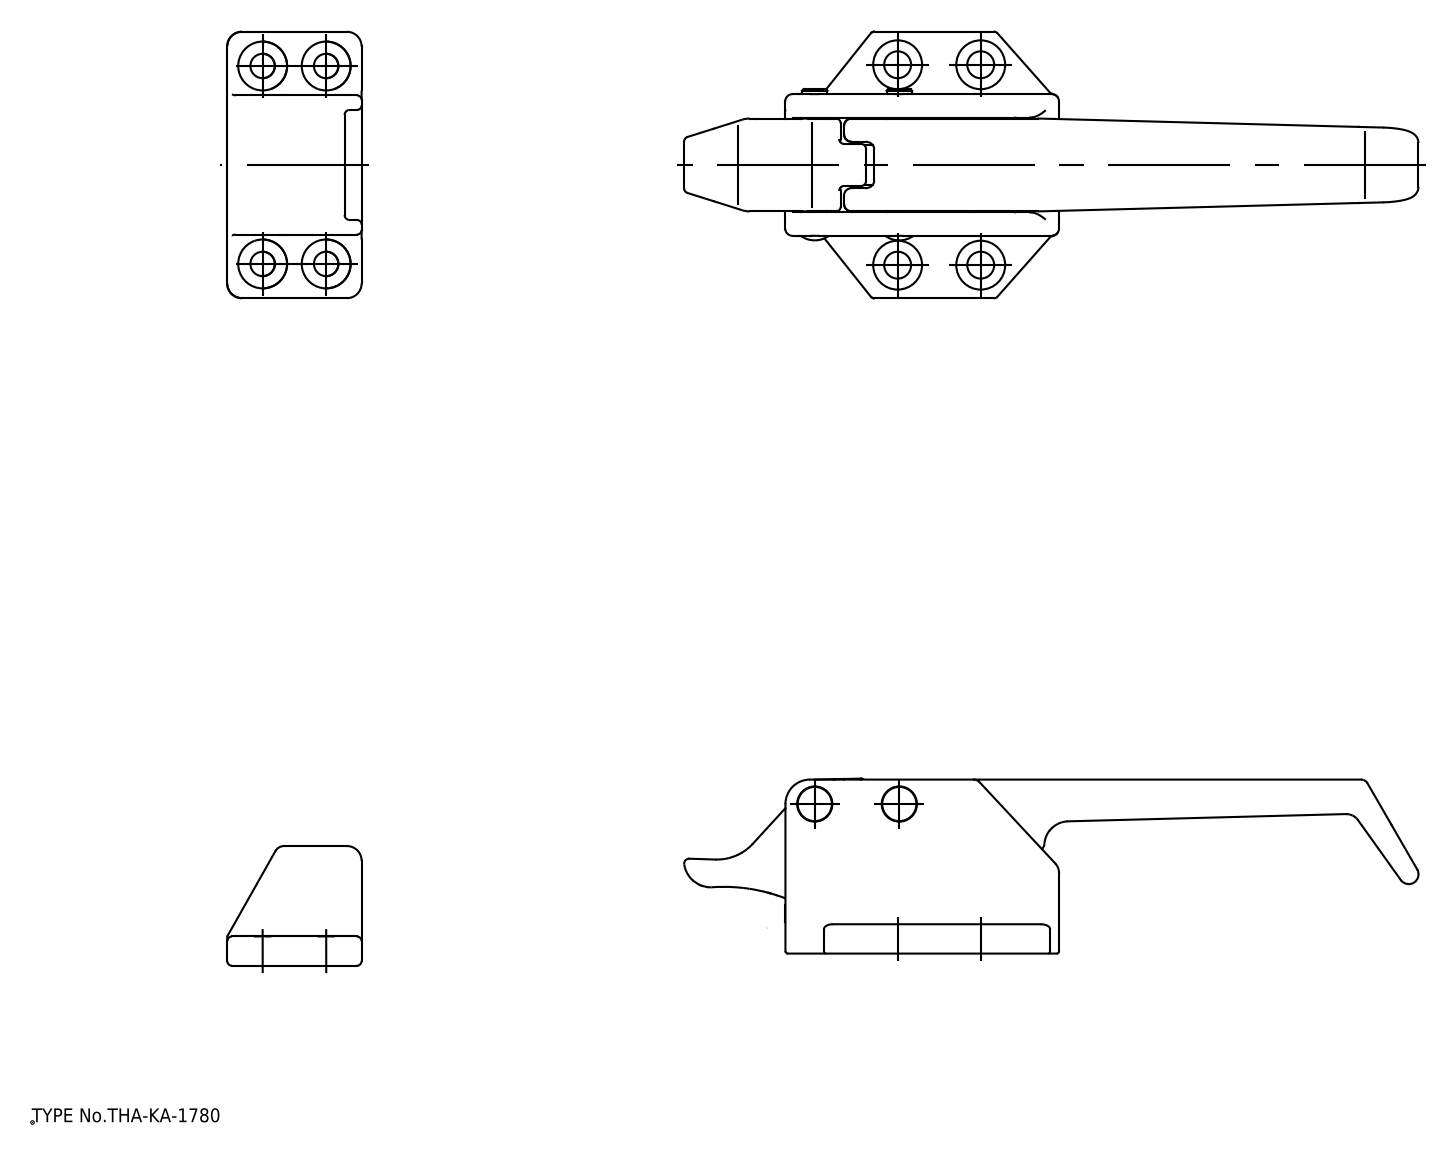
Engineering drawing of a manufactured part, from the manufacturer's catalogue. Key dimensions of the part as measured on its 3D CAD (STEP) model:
Part name (STEP PRODUCT): ボディー; リンク; ハンドル; ストライク (+2 more)
STEP written by: spGate 16.7.1 (AUTOMOTIVE_DESIGN)
Units: millimetres
Bodies: 7 solids, 876 faces (127 planar, 372 cylindrical, 377 other)
Overall size (bounding box): 164.29 × 54.5 × 35.86
Volume: 61 793 mm³ · Surface area: 32 510 mm²
Round holes (diameter × count): ⌀5 ×9, ⌀10 ×8, ⌀5.5 ×4, ⌀5.2 ×2, ⌀7.2 ×2
Round bosses / shafts (diameter × count): ⌀7 ×2
Partial cylindrical surfaces — rounded edges, fillets, slot ends (radius × count): R1 ×147, R1.5 ×43, R0.5 ×33, R2 ×18, R3 ×13, R5 ×10, R4.8 ×2, R1.75 ×1
Main face-to-face distances: 4.8, 24.2, 29, 5, 24, 19.2, 19.4, 3, 4.75, 19
Hole centre spacings: 41, 44.38, 17, 13, 16.99, 17.01, 37.99, 38
